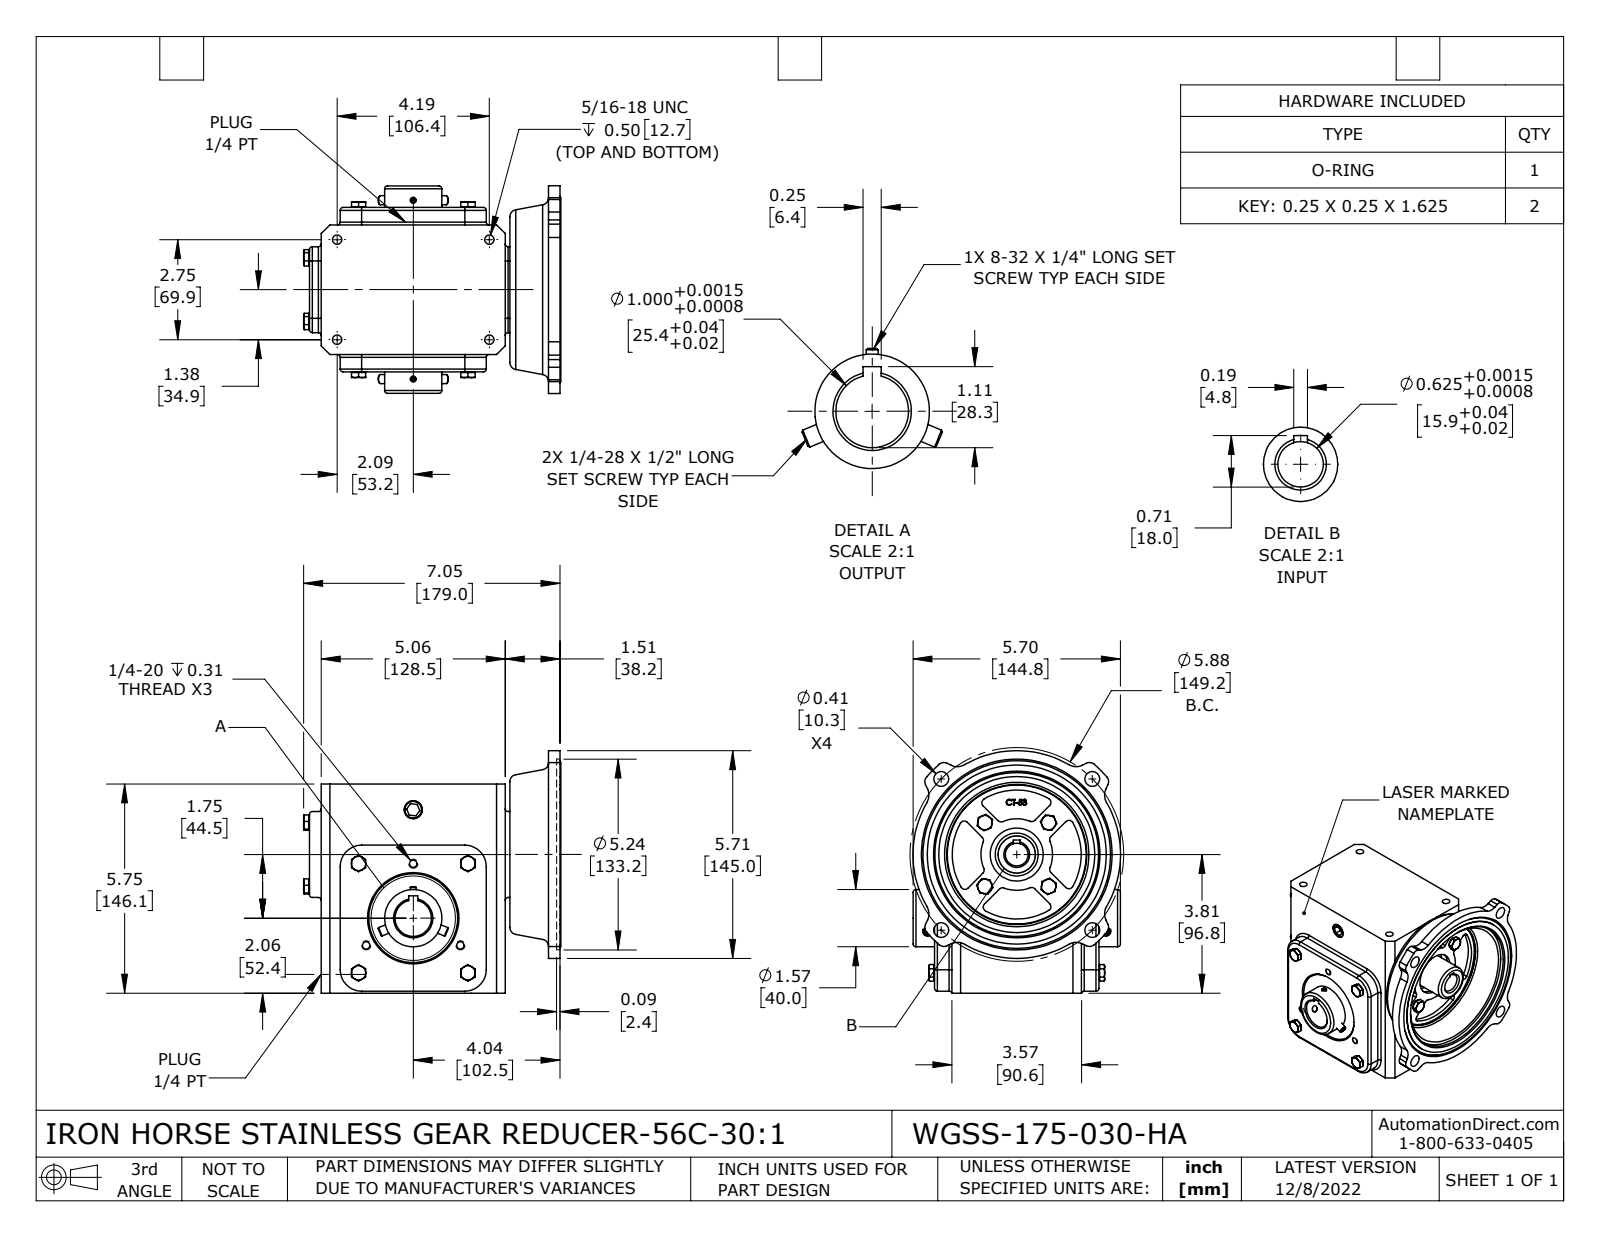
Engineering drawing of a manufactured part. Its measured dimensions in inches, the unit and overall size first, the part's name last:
Units: inches
Overall size (bounding box): 7.071 × 6.691 × 5.709
Round holes (diameter × count): ⌀0.213 ×4, ⌀0.257 ×4, ⌀0.406 ×4, ⌀0.201 ×3, ⌀0.136 ×2, ⌀0.625 ×1, ⌀0.866 ×1, ⌀1 ×1, ⌀1.102 ×1, ⌀1.457 ×1, ⌀1.575 ×1, ⌀3.819 ×1
Round bosses / shafts (diameter × count): ⌀0.394 ×8, ⌀0.25 ×4, ⌀0.164 ×2, ⌀4.921 ×1, ⌀2.441 ×1, ⌀1.575 ×1, ⌀1.181 ×1
Partial cylindrical surfaces — rounded edges, fillets, slot ends (radius × count): R0.079 ×28, R0.118 ×16, R0.394 ×12, R0.197 ×8, R0.591 ×4, R0.984 ×1, R1.772 ×1, R2.854 ×1
Main face-to-face distances: 0.48, 4.04, 5.75, 5.06, 0.157, 3.56, 4.52, 0.315, 6.565, 1.506
Hole centre spacings: 2.357, 2.937, 4.154, 1.496, 2.591, 4.913, 2.75, 4.188
Volume: 127 in³ · Surface area: 281 in²
Bodies: 7 solids, 891 faces (390 planar, 231 cylindrical, 270 other)
Part name (STEP PRODUCT): WGSS-175-030-HA
STEP written by: SolidWorks 2021 (CONFIG_CONTROL_DESIGN)
